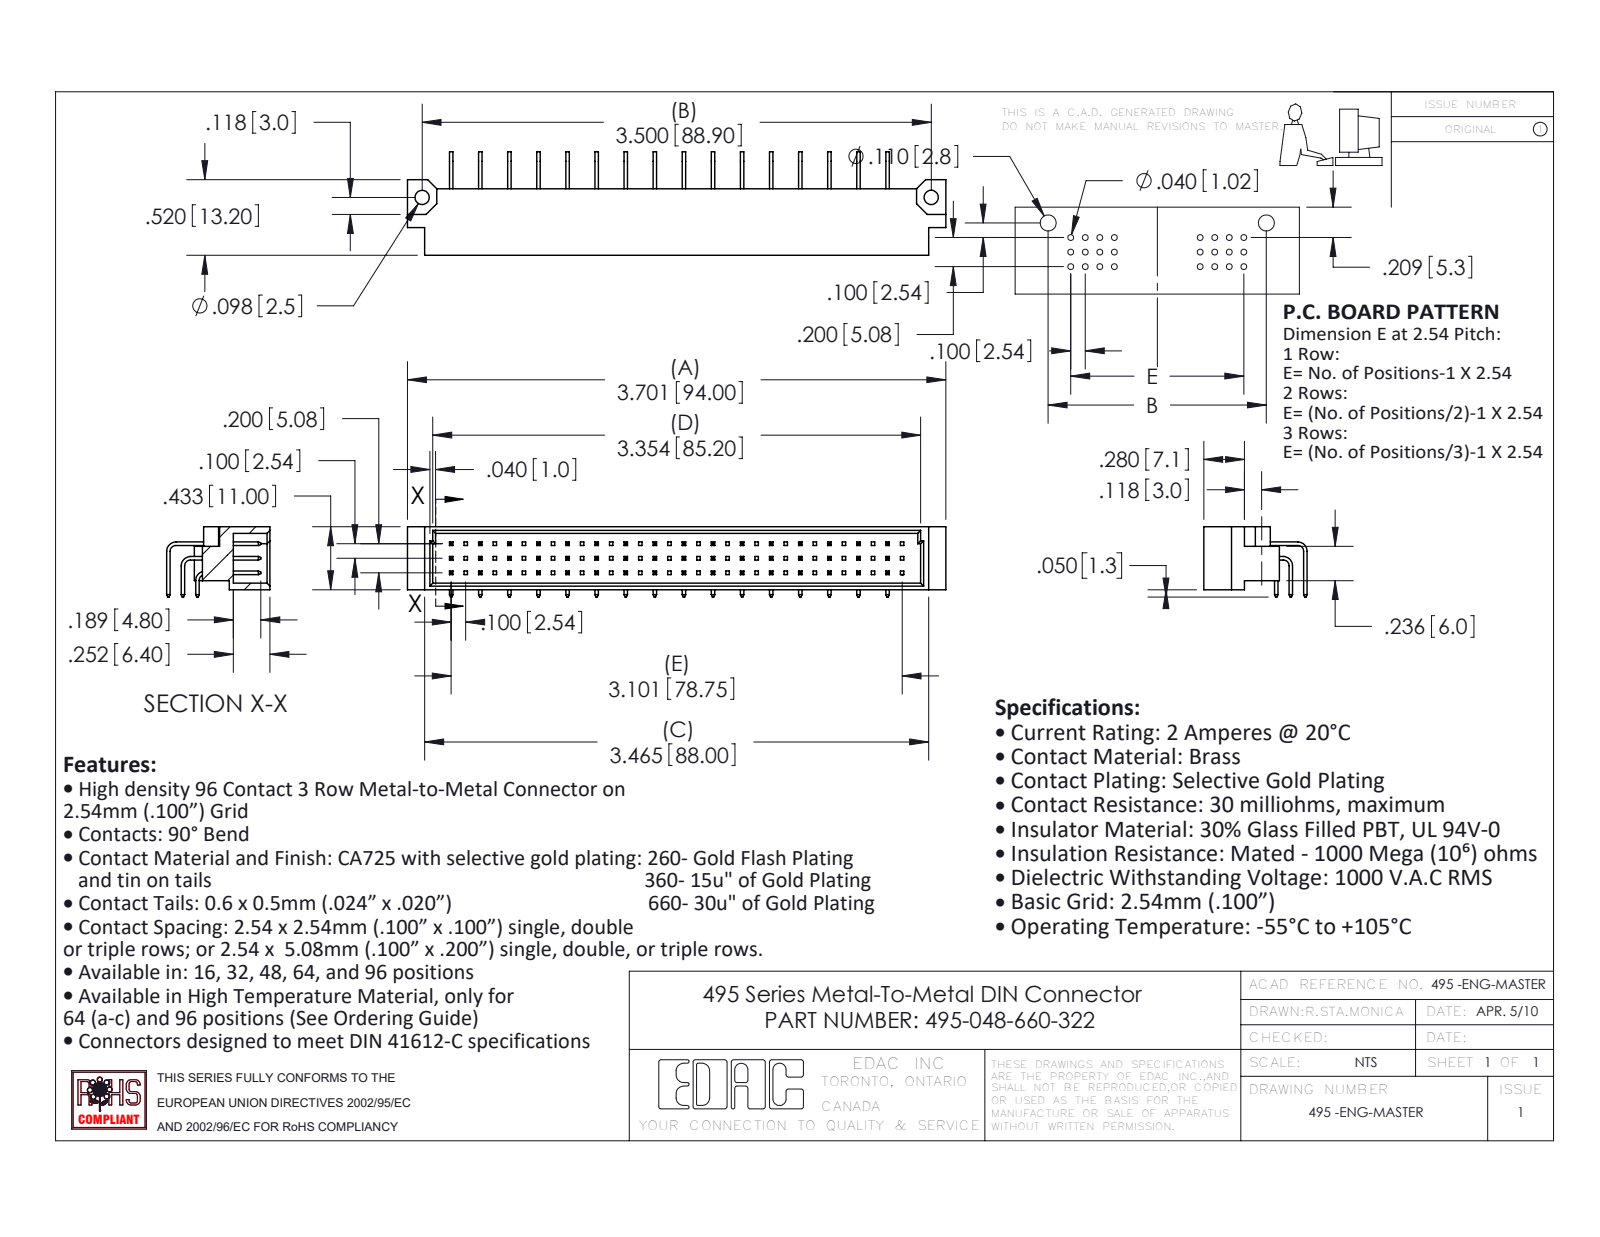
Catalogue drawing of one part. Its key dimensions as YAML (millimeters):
part_name: "495 Part_96; 495-048-660-322; 495-290-3; 495-290-2 (+1 more)"
step_written_by: "SolidWorks 2020 (AUTOMOTIVE_DESIGN)"
units: millimeters
bodies: {solids: 49, faces: 1297, planar: 1197, cylindrical: 100, other: 0}
overall_size: [94, 18.05, 12.27]
volume: 6276
surface_area: 9144
round_holes:
  - {diameter: 2.49, count: 2}
partial_cylinders:
  - {radius: 1.02, count: 3}
  - {radius: 1.65, count: 3}
face_to_face_distances: [5.08, 1.14, 9.86, 2.54, 5.2, 0.61, 11, 10.16, 15.24, 20.32]
hole_center_spacings: [88.9]
